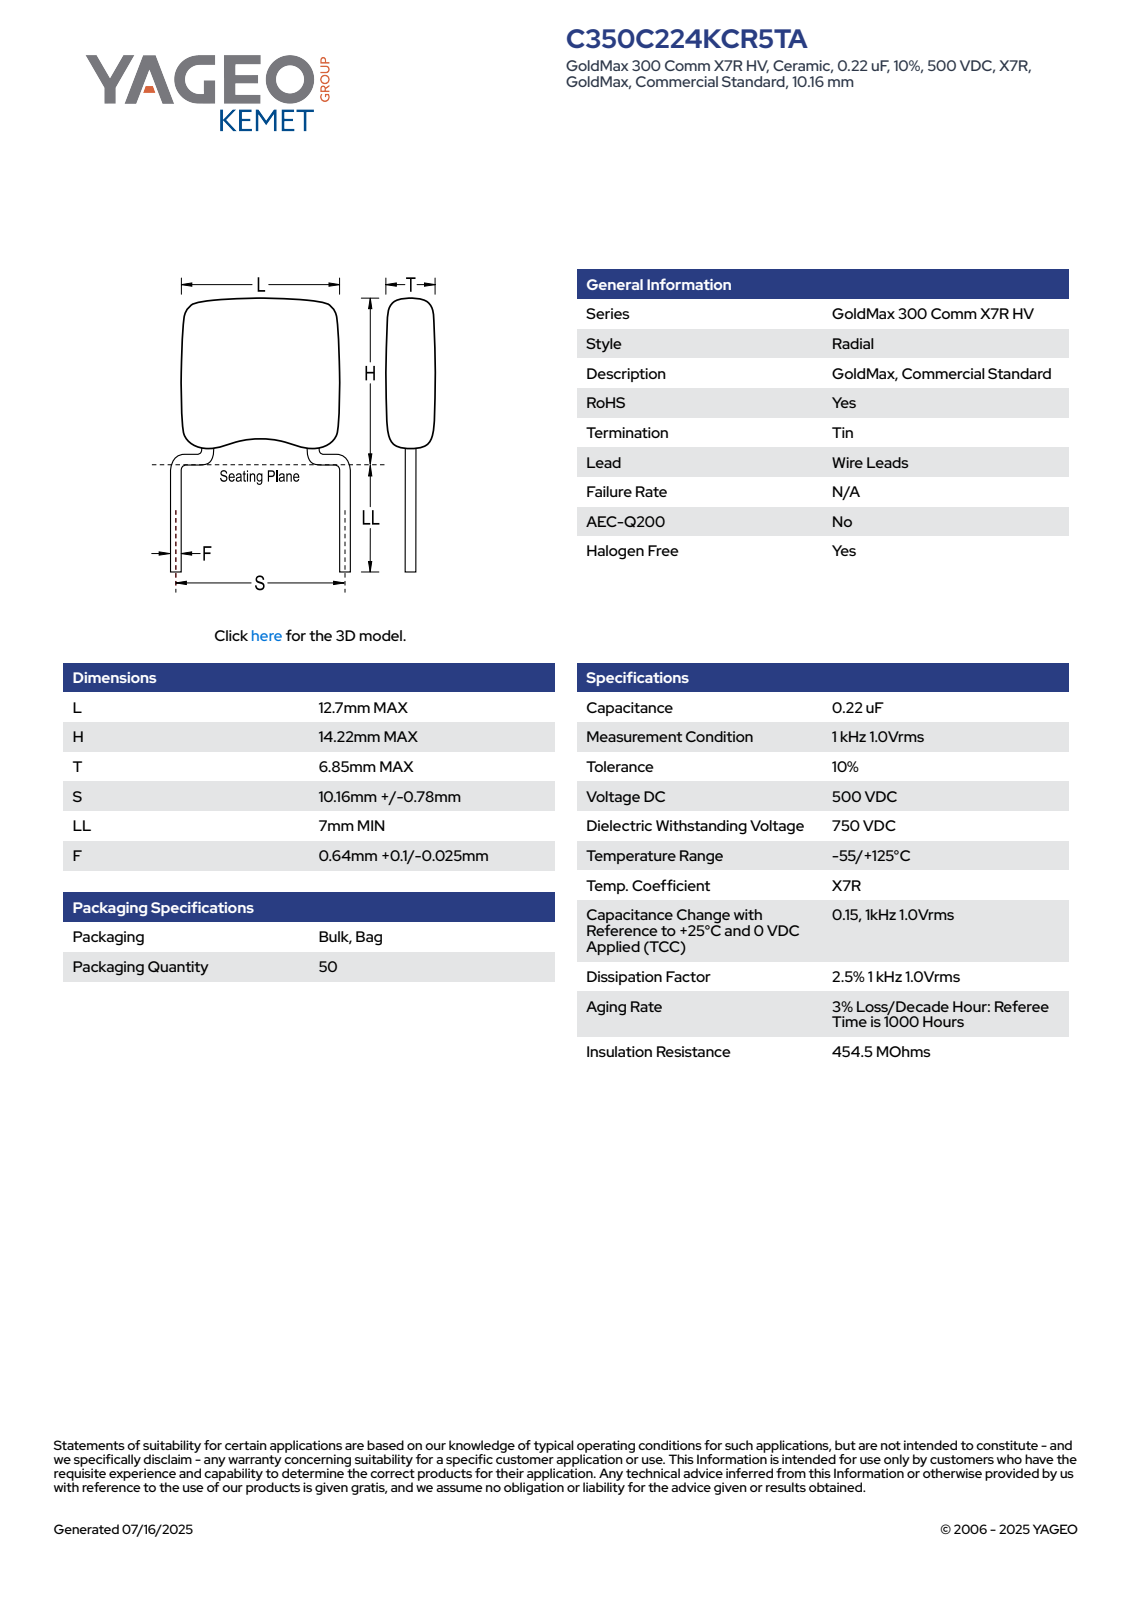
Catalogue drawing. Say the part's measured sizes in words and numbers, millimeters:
The part is named "CCR_SB_12.7X14.22_L12.7H14.22T6.85S10.16LL7F0.64". Its 3-D file was written by "SolidWorks 2014 (AUTOMOTIVE_DESIGN)". It is 4 solids with 97 faces: 65 planar, 14 cylindrical and 18 other. Overall it measures 21.22 by 12.7 by 6.86 millimeters. Its volume is 1 029 cubic millimeters and its surface area 641 square millimeters. Round bosses or shafts: 2 of diameter 0.64. Partial cylindrical surfaces (rounded edges, fillets, slot ends): 10 of radius 1. The main face-to-face distances are 6.85, 12.03, 12.7, 1.08, 6.6, 5.43, 5.52, 6.51, 0.47, 0.67.
